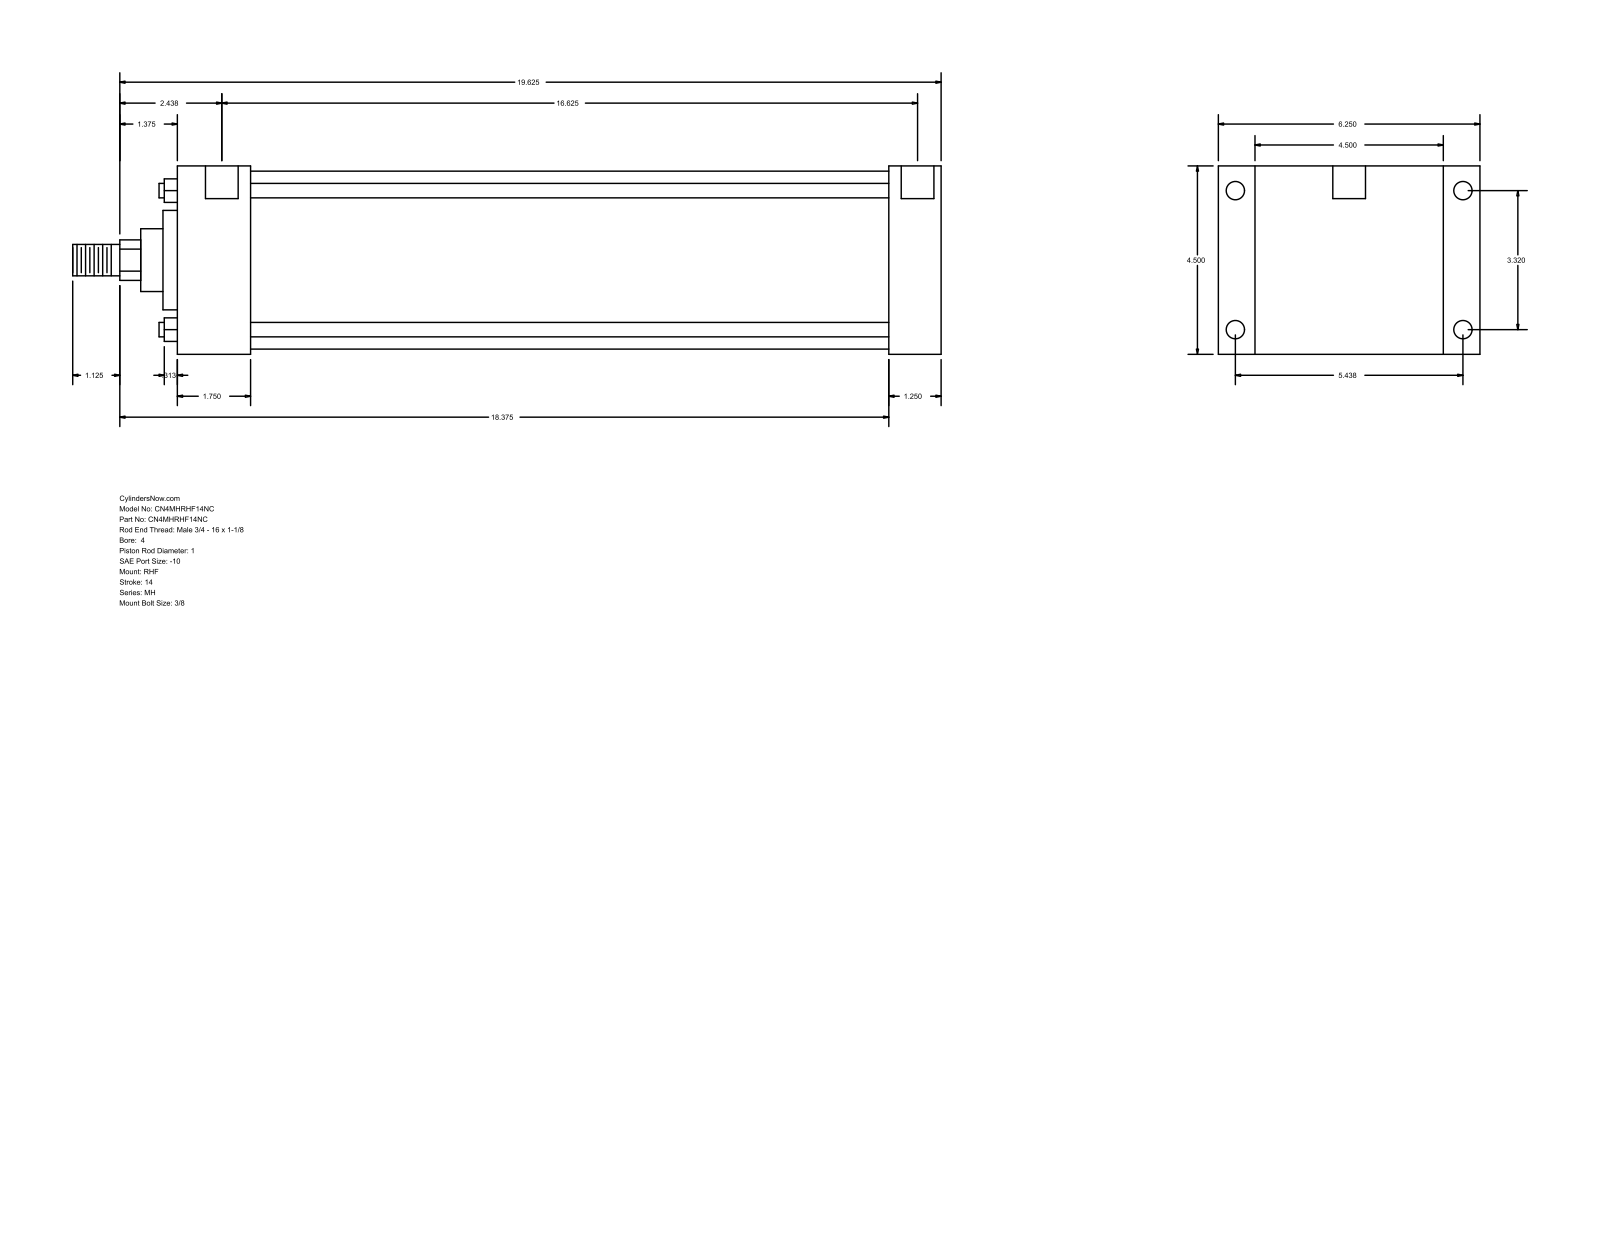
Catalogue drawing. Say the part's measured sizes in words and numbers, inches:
The part is named "MH_RHF__0400_1". Its 3-D file was written by "GSSL Pune (CONFIG_CONTROL_DESIGN)". It is 0 solids with 90 faces: 61 planar, 29 cylindrical and 0 other. Overall it measures 20.75 by 6.25 by 4.5 inches. Round holes: 4 of diameter 0.344, 4 of diameter 0.438, 2 of diameter 0.781. Round bosses or shafts: 4 of diameter 0.345, 1 of diameter 4.25, 1 of diameter 2.375, 1 of diameter 1.5, 1 of diameter 1, 1 of diameter 0.75. Partial cylindrical surfaces (rounded edges, fillets, slot ends): 1 of radius 0.484. The main face-to-face distances are 4.5, 18.25, 17, 1.25, 0.875, 5.375, 1.75, 15.25, 16.5, 6.25. The hole center spacings are 0.062, 3.32, 5.438, 6.371, 16.687, 16.75, 16.625.
